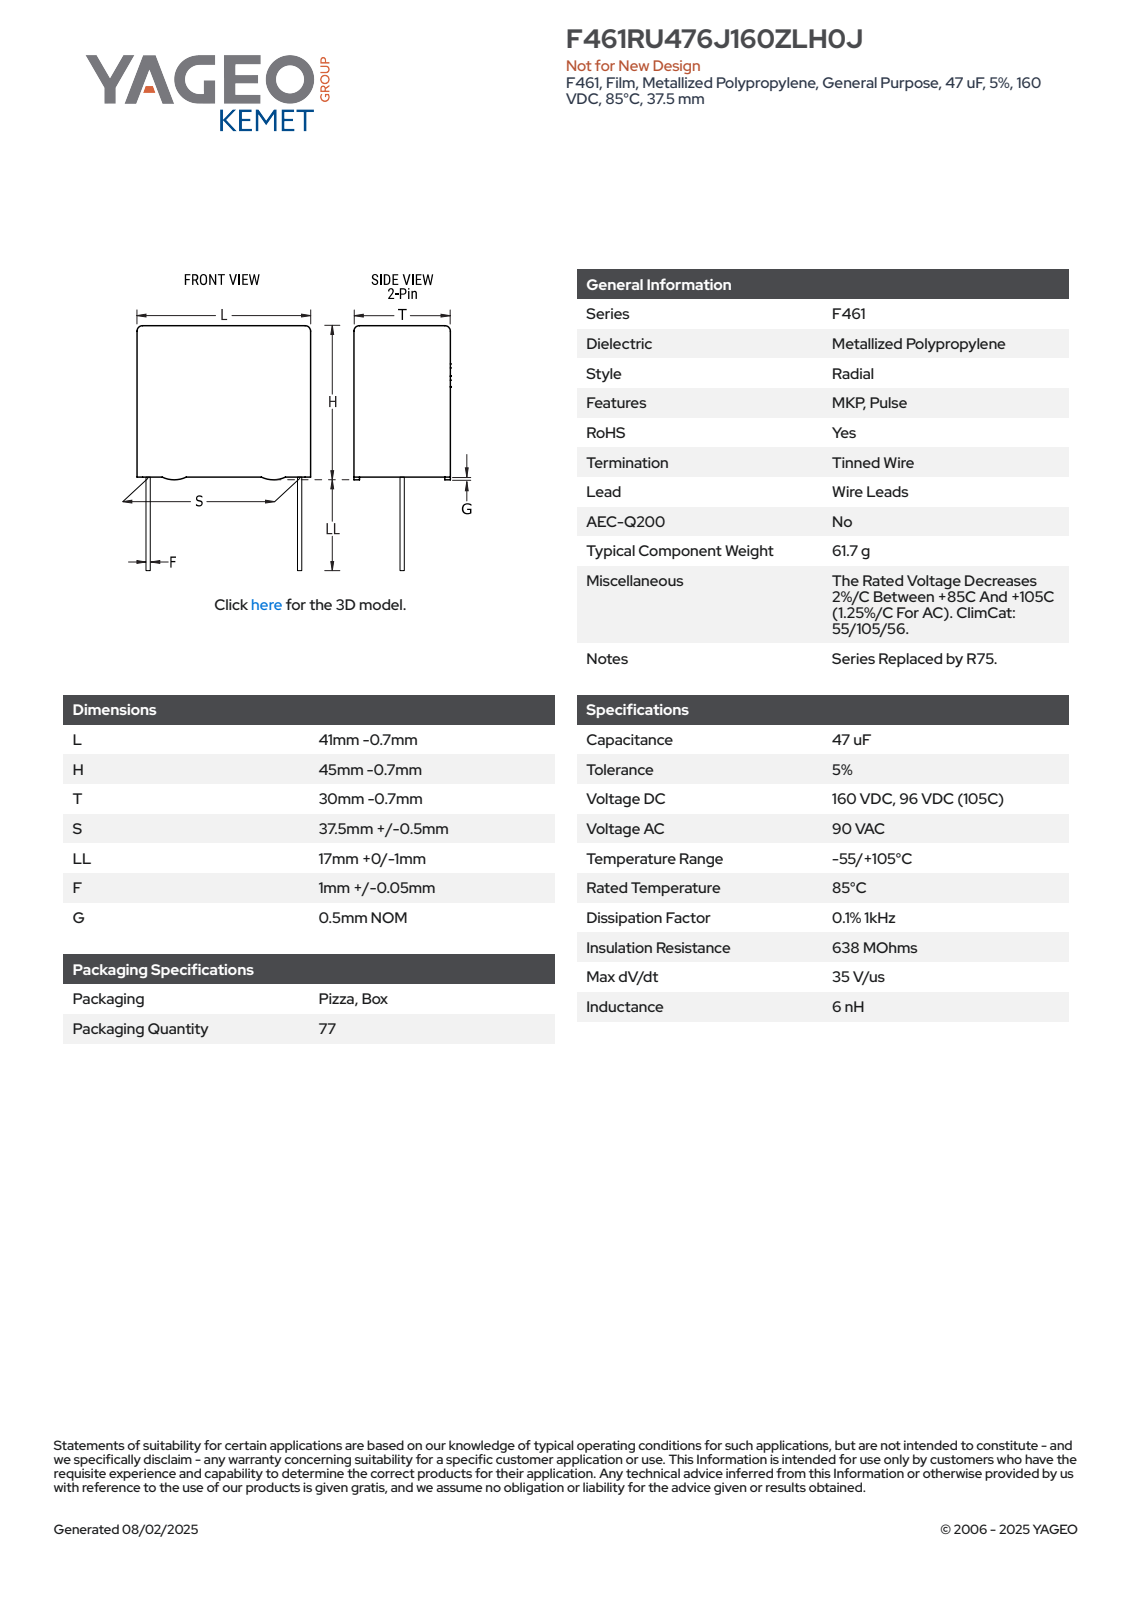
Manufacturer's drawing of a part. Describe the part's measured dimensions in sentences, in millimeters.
The part is named "CFR_RBG_41X45X30_L40.3H44.3T29.3S37.5LL17F1.05G0.5". Its 3-D file was written by "SolidWorks 2014 (AUTOMOTIVE_DESIGN)". It is 4 solids with 89 faces: 81 planar, 8 cylindrical and 0 other. Overall it measures 61.3 by 40.3 by 29.3 millimeters. Its volume is 51 763 cubic millimeters and its surface area 8 749 square millimeters. Round bosses or shafts: 2 of diameter 1.05. Partial cylindrical surfaces (rounded edges, fillets, slot ends): 4 of radius 0.5. The main face-to-face distances are 29.3, 40.3, 43.8, 0.5, 44.3, 1.67, 27.63, 25.96, 23.55, 23.56.
